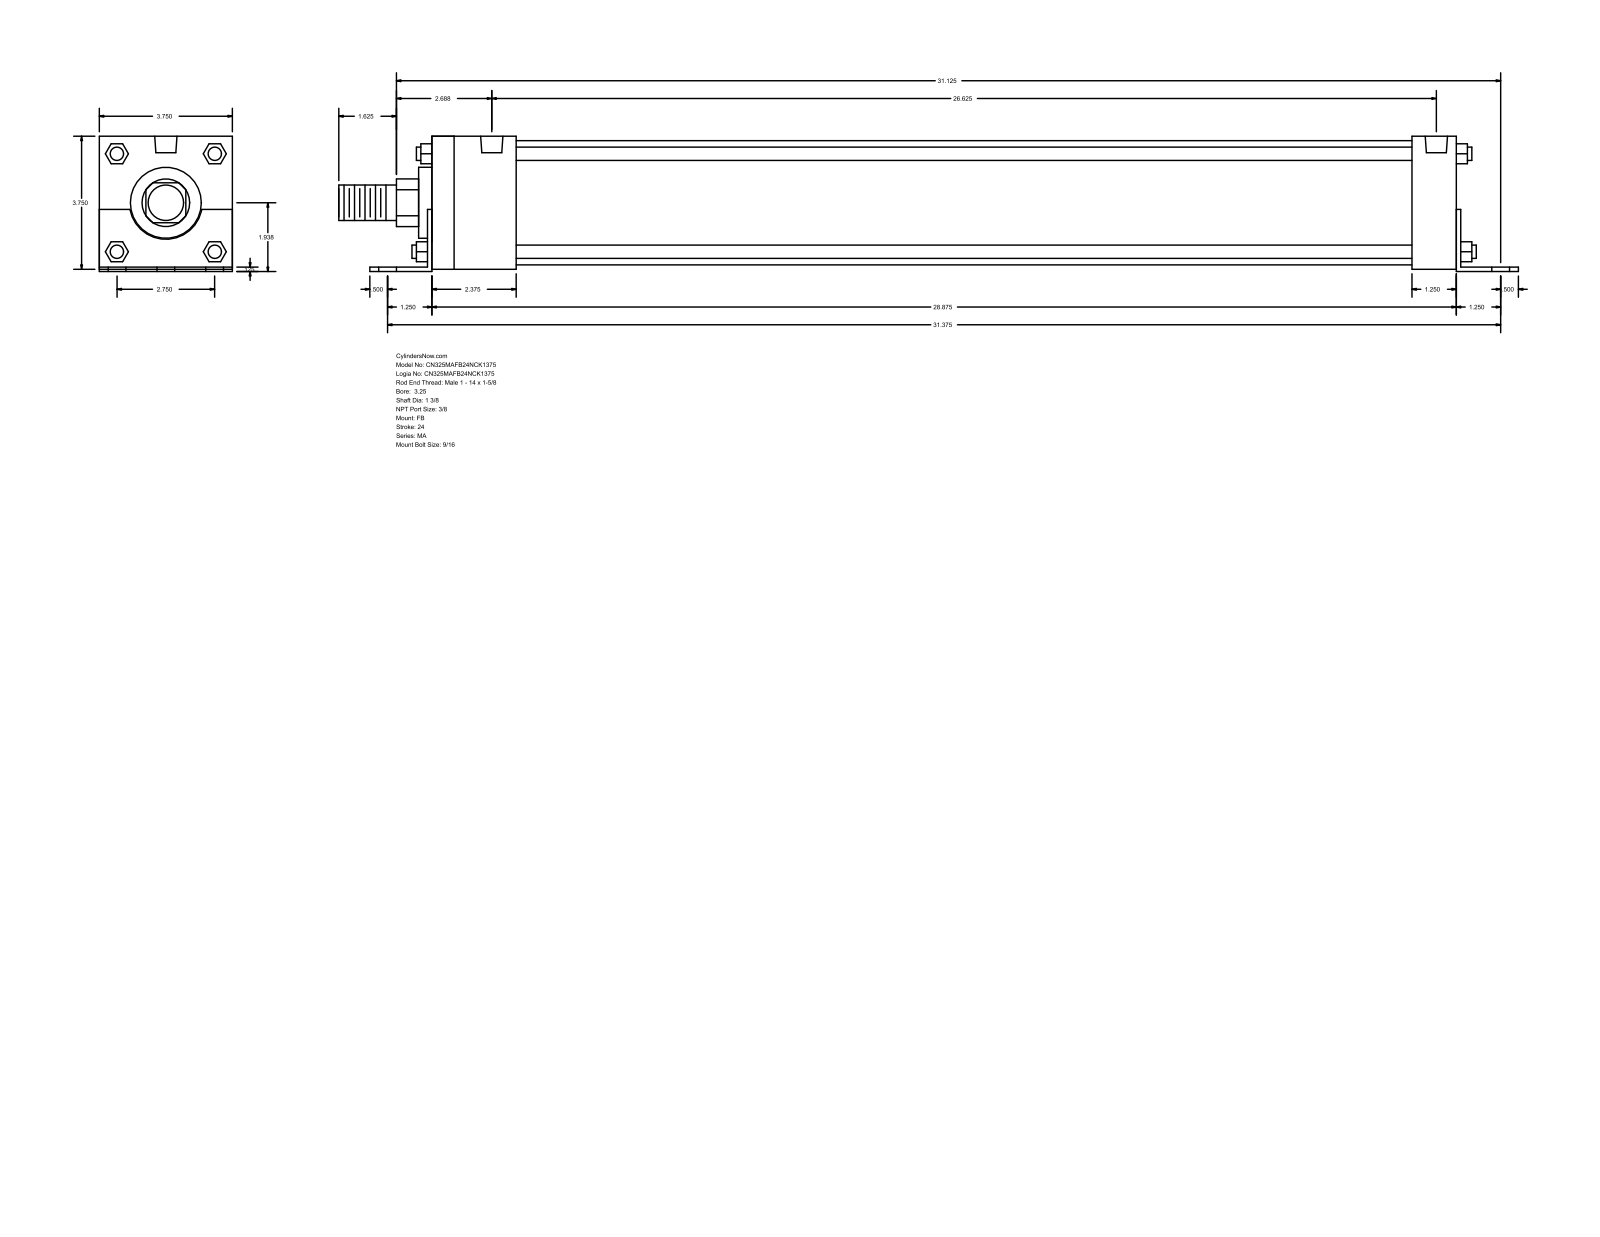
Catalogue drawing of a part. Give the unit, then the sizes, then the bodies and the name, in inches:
Units: inches
Overall size (bounding box): 33.25 × 3.813 × 3.75
Round holes (diameter × count): ⌀0.563 ×6, ⌀0.437 ×4, ⌀0.627 ×2
Round bosses / shafts (diameter × count): ⌀0.375 ×4, ⌀3.5 ×1, ⌀2 ×1, ⌀1.375 ×1, ⌀1 ×1
Partial cylindrical surfaces — rounded edges, fillets, slot ends (radius × count): R0.672 ×1, R1.03 ×1
Main face-to-face distances: 3.75, 0.125, 0.063, 3.812, 0.062, 3.687, 29, 28.875, 1.25, 1.375
Hole centre spacings: 1.375, 31.405, 31.375, 0.188, 2.275, 2.427, 2.75, 3.243
Bodies: 0 solids, 140 faces (105 planar, 35 cylindrical, 0 other)
Part name (STEP PRODUCT): MA_FB__0325_1.375
STEP written by: GSSL Pune (CONFIG_CONTROL_DESIGN)
